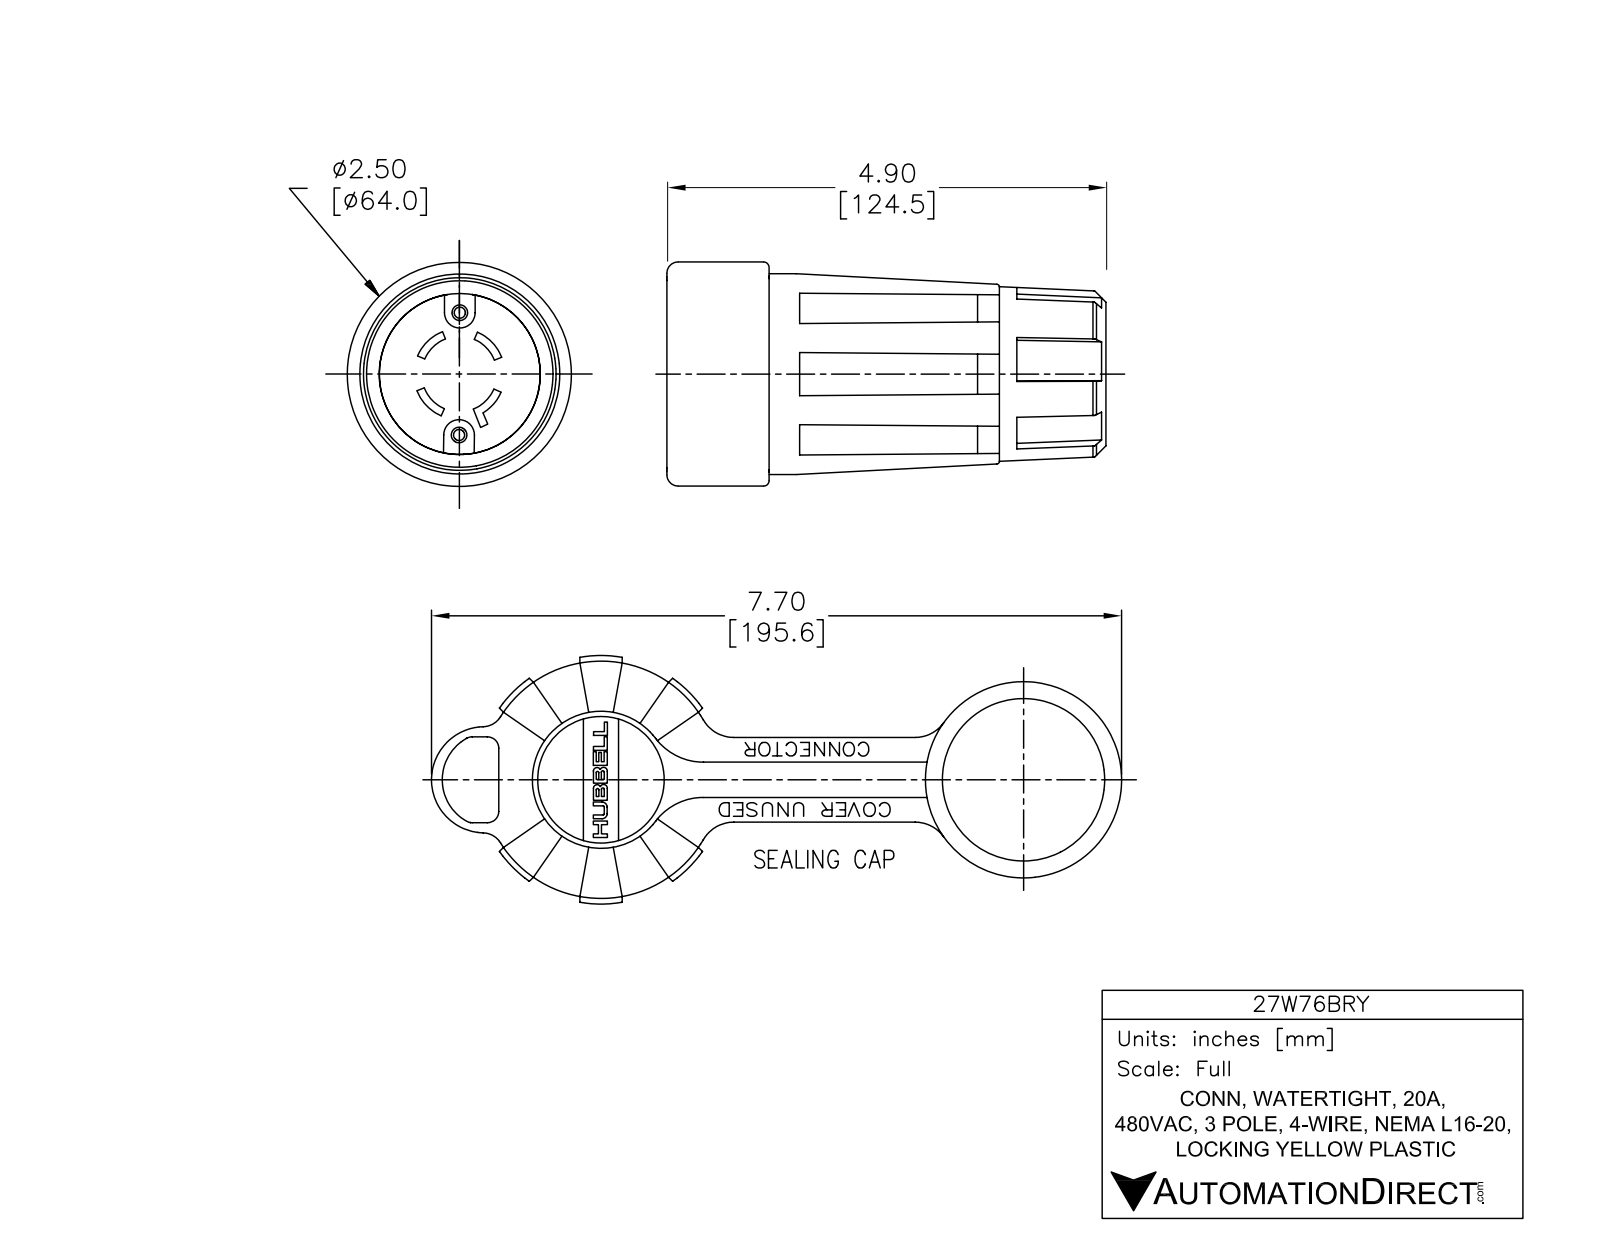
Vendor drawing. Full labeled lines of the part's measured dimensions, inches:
Part name (STEP PRODUCT): 27W76BRY
STEP written by: SolidWorks 2013 (AUTOMOTIVE_DESIGN)
Units: inches
Bodies: 1 solid, 359 faces (137 planar, 98 cylindrical, 124 other)
Overall size (bounding box): 8.08 × 4.966 × 3.139
Volume: 20.16 in³ · Surface area: 104.7 in²
Round holes (diameter × count): ⌀0.95 ×1, ⌀1.82 ×1, ⌀1.86 ×1, ⌀2.345 ×1, ⌀2.805 ×1
Round bosses / shafts (diameter × count): ⌀0.2 ×2, ⌀2.76 ×1, ⌀2.755 ×1, ⌀2.43 ×1, ⌀2.25 ×1, ⌀1.975 ×1, ⌀1.415 ×1
Partial cylindrical surfaces — rounded edges, fillets, slot ends (radius × count): R0.015 ×16, R0.061 ×8, R0.25 ×6, R1.57 ×6, R0.1 ×2, R0.11 ×2, R0.4 ×1, R0.402 ×1
Main face-to-face distances: 0.08, 0.38, 0.67, 0.75, 0.06, 0.81, 0.14, 0.13, 2.685, 2.555
Hole centre spacings: 4.7
